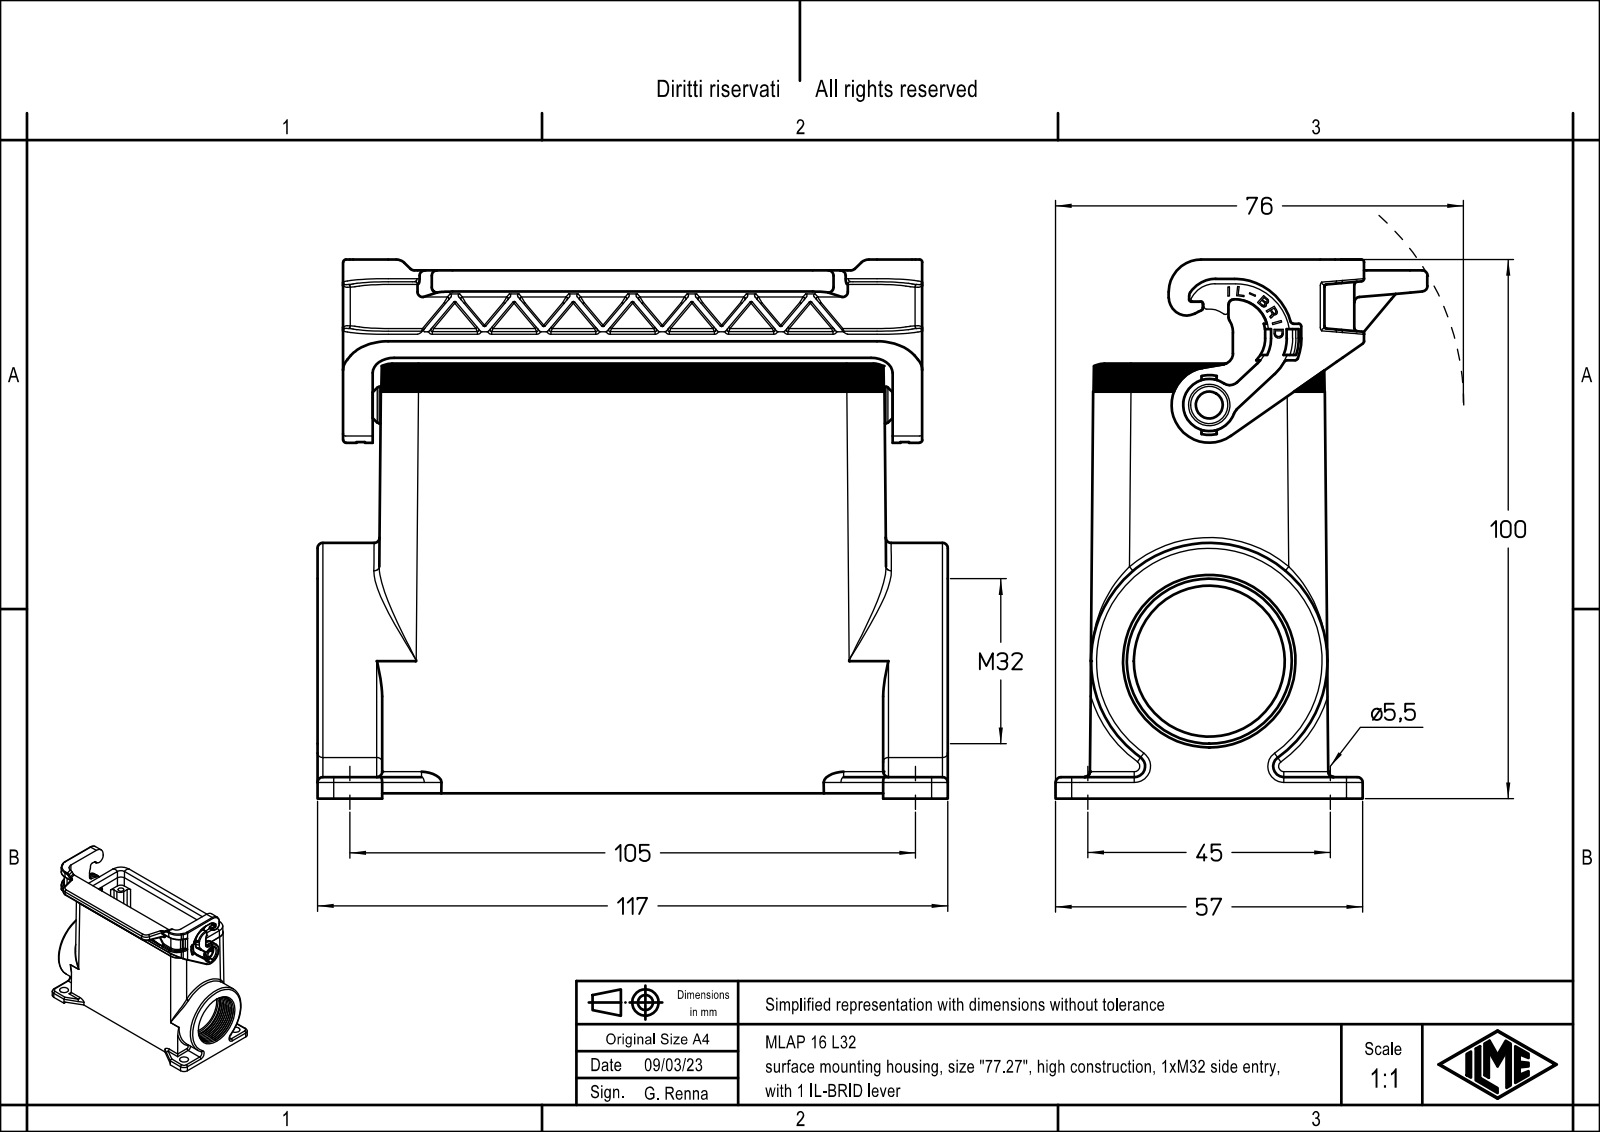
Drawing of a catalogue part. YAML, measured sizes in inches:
part_name: "MLAP 16 L32"
step_written_by: "Creo Elements/Direct Modeling 20.1B 02-Apr-2019 (C) Parametric Technology GmbH (AUTOMOTIVE_DESIGN)"
units: inches
bodies: {solids: 1, faces: 1057, planar: 638, cylindrical: 287, other: 132}
overall_size: [4.606, 3.937, 2.717]
volume: 9.296
surface_area: 106.5
round_holes:
  - {diameter: 0.118, count: 4}
  - {diameter: 0.138, count: 4}
  - {diameter: 0.217, count: 3}
  - {diameter: 0.128, count: 1}
  - {diameter: 0.213, count: 1}
  - {diameter: 0.303, count: 1}
  - {diameter: 1.102, count: 1}
  - {diameter: 1.205, count: 1}
round_bosses_or_shafts:
  - {diameter: 1.727, count: 1}
  - {diameter: 0.272, count: 1}
  - {diameter: 0.268, count: 1}
  - {diameter: 0.205, count: 1}
  - {diameter: 0.126, count: 1}
partial_cylinders:
  - {radius: 0.004, count: 27}
  - {radius: 0.118, count: 16}
  - {radius: 0.008, count: 15}
  - {radius: 0.039, count: 15}
  - {radius: 0.02, count: 11}
  - {radius: 0.079, count: 11}
  - {radius: 0.276, count: 10}
  - {radius: 0.059, count: 9}
face_to_face_distances: [0.118, 0.404, 4.203, 0.039, 3.819, 3.701, 0.157, 0.276, 4.016, 0.148]
hole_center_spacings: [0.647, 1.517, 3.61, 3.862, 1.063, 3.051, 3.231, 1.772]
